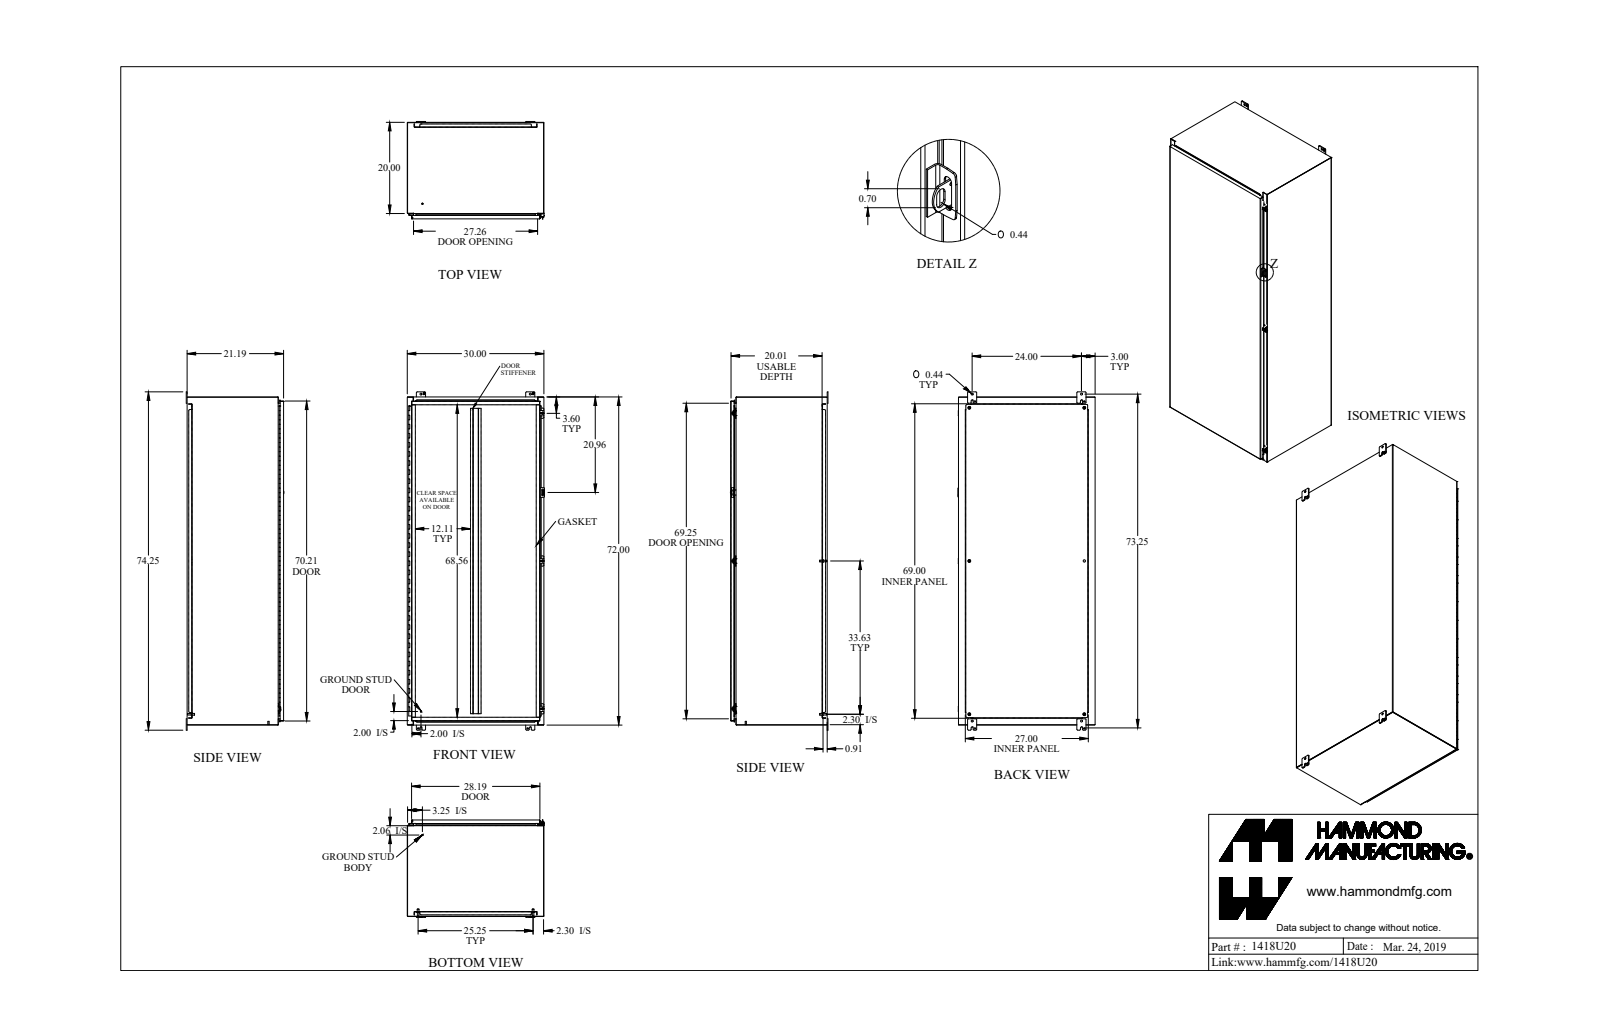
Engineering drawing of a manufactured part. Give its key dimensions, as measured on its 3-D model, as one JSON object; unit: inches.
{"part_name": "1418U20_Default", "step_written_by": "SolidWorks 2019 (CONFIG_CONTROL_DESIGN)", "units": "inches", "bodies": {"solids": 50, "faces": 1846, "planar": 1008, "cylindrical": 778, "other": 60}, "overall_size": [74.25, 30.128, 21.437], "volume_in3": 899, "surface_area_in2": 23423, "round_holes": [[0.304, 12], [0.5, 6], [0.307, 4], [0.313, 4], [0.437, 4], [0.445, 4], [0.213, 3], [0.265, 3], [0.375, 3], [0.11, 1], [0.125, 1]], "round_bosses_or_shafts": [[0.65, 6], [0.375, 6], [0.33, 6], [1, 4], [0.5, 3], [0.39, 3], [0.244, 3], [0.281, 2]], "partial_cylinders_radius": [[0.188, 38], [0.036, 22], [0.108, 22], [0.25, 20], [0.048, 19], [0.143, 19], [0.116, 16], [0.125, 8]], "face_to_face_distances": [0.072, 21.113, 29.928, 21.041, 21.185, 0.095, 20.081, 20.009, 1.032, 1.104], "hole_center_spacings": [24, 6, 12, 18, 30, 36, 33.625, 42]}
